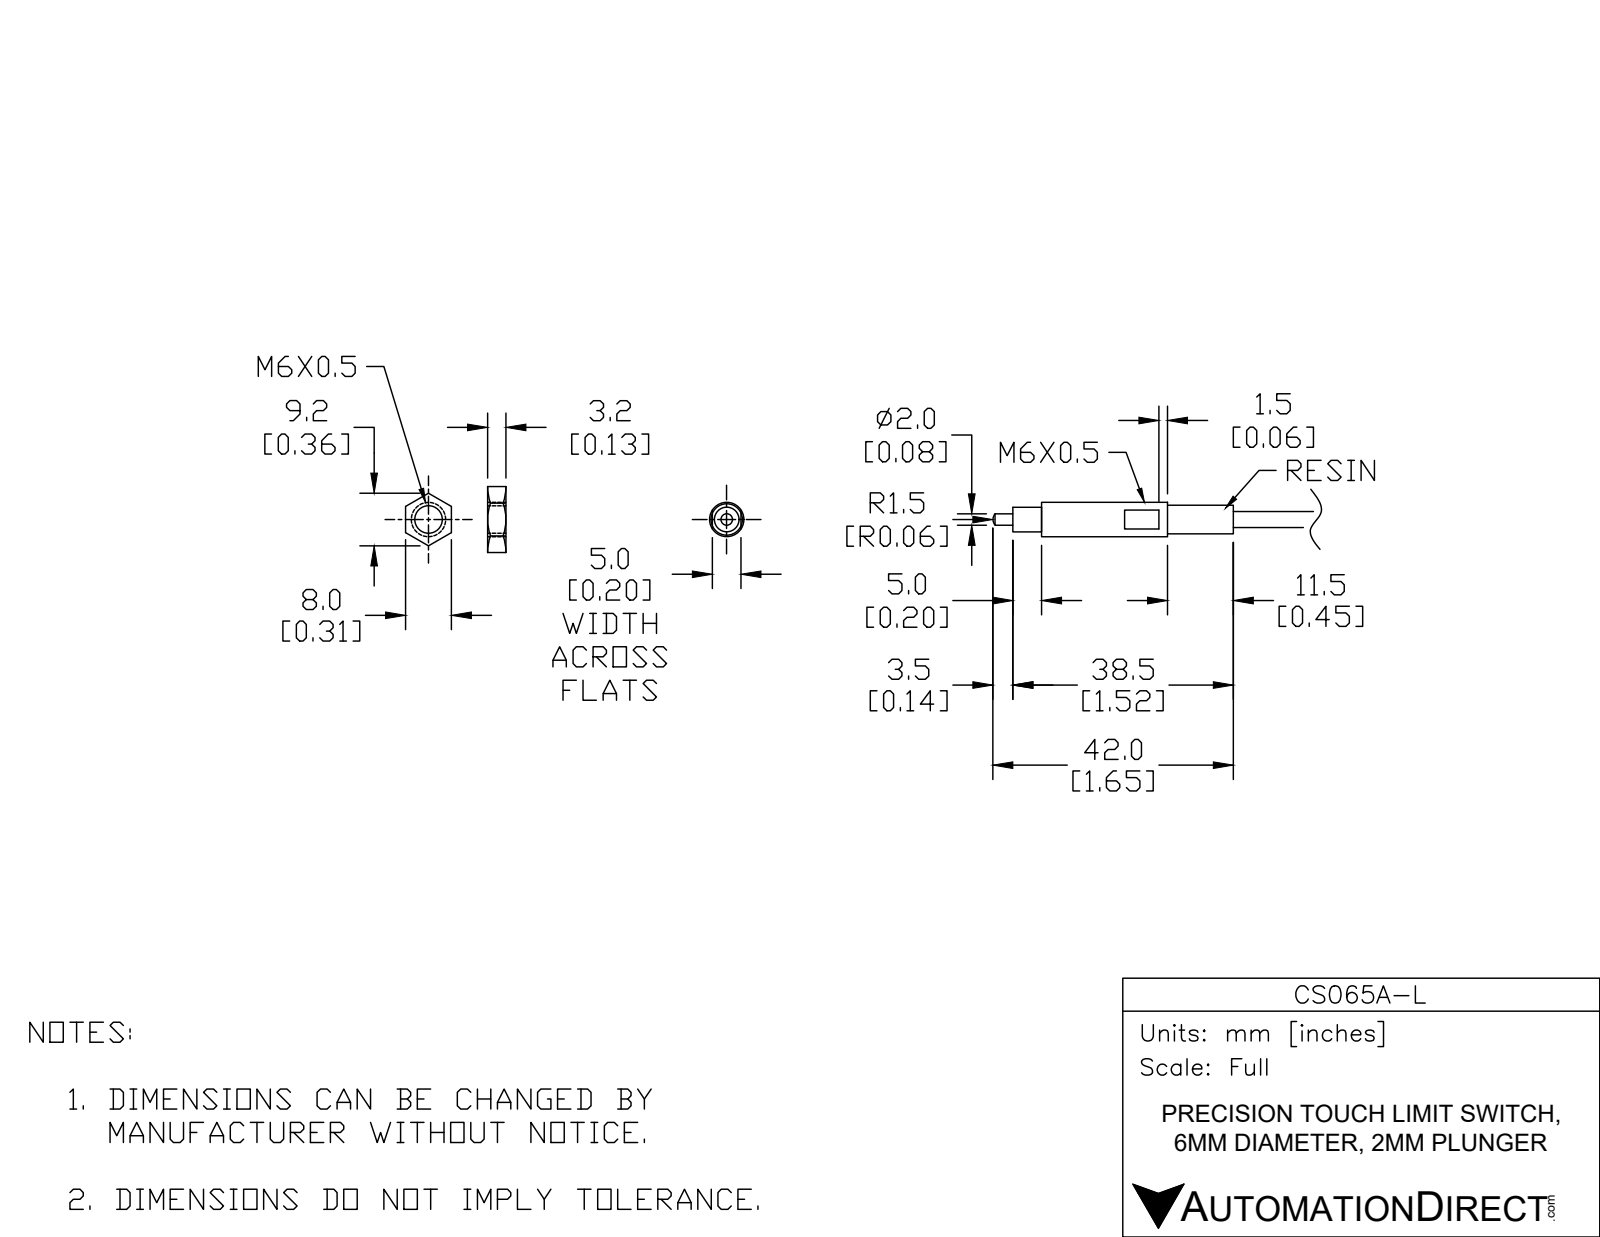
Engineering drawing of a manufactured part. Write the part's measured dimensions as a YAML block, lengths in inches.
part_name: "CS065A-L - 1"
step_written_by: "SolidWorks 2017 (AUTOMOTIVE_DESIGN)"
units: inches
bodies: {solids: 1, faces: 183, planar: 11, cylindrical: 97, other: 75}
overall_size: [2.205, 0.236, 0.236]
volume: 0.058
surface_area: 1.738
round_bosses_or_shafts:
  - {diameter: 0.236, count: 1}
  - {diameter: 0.197, count: 1}
  - {diameter: 0.169, count: 1}
  - {diameter: 0.11, count: 1}
  - {diameter: 0.079, count: 1}
face_to_face_distances: [0.197, 1.516, 1.319, 1.004, 1.063, 2.067, 1.87, 0.551, 0.866, 0.453]
